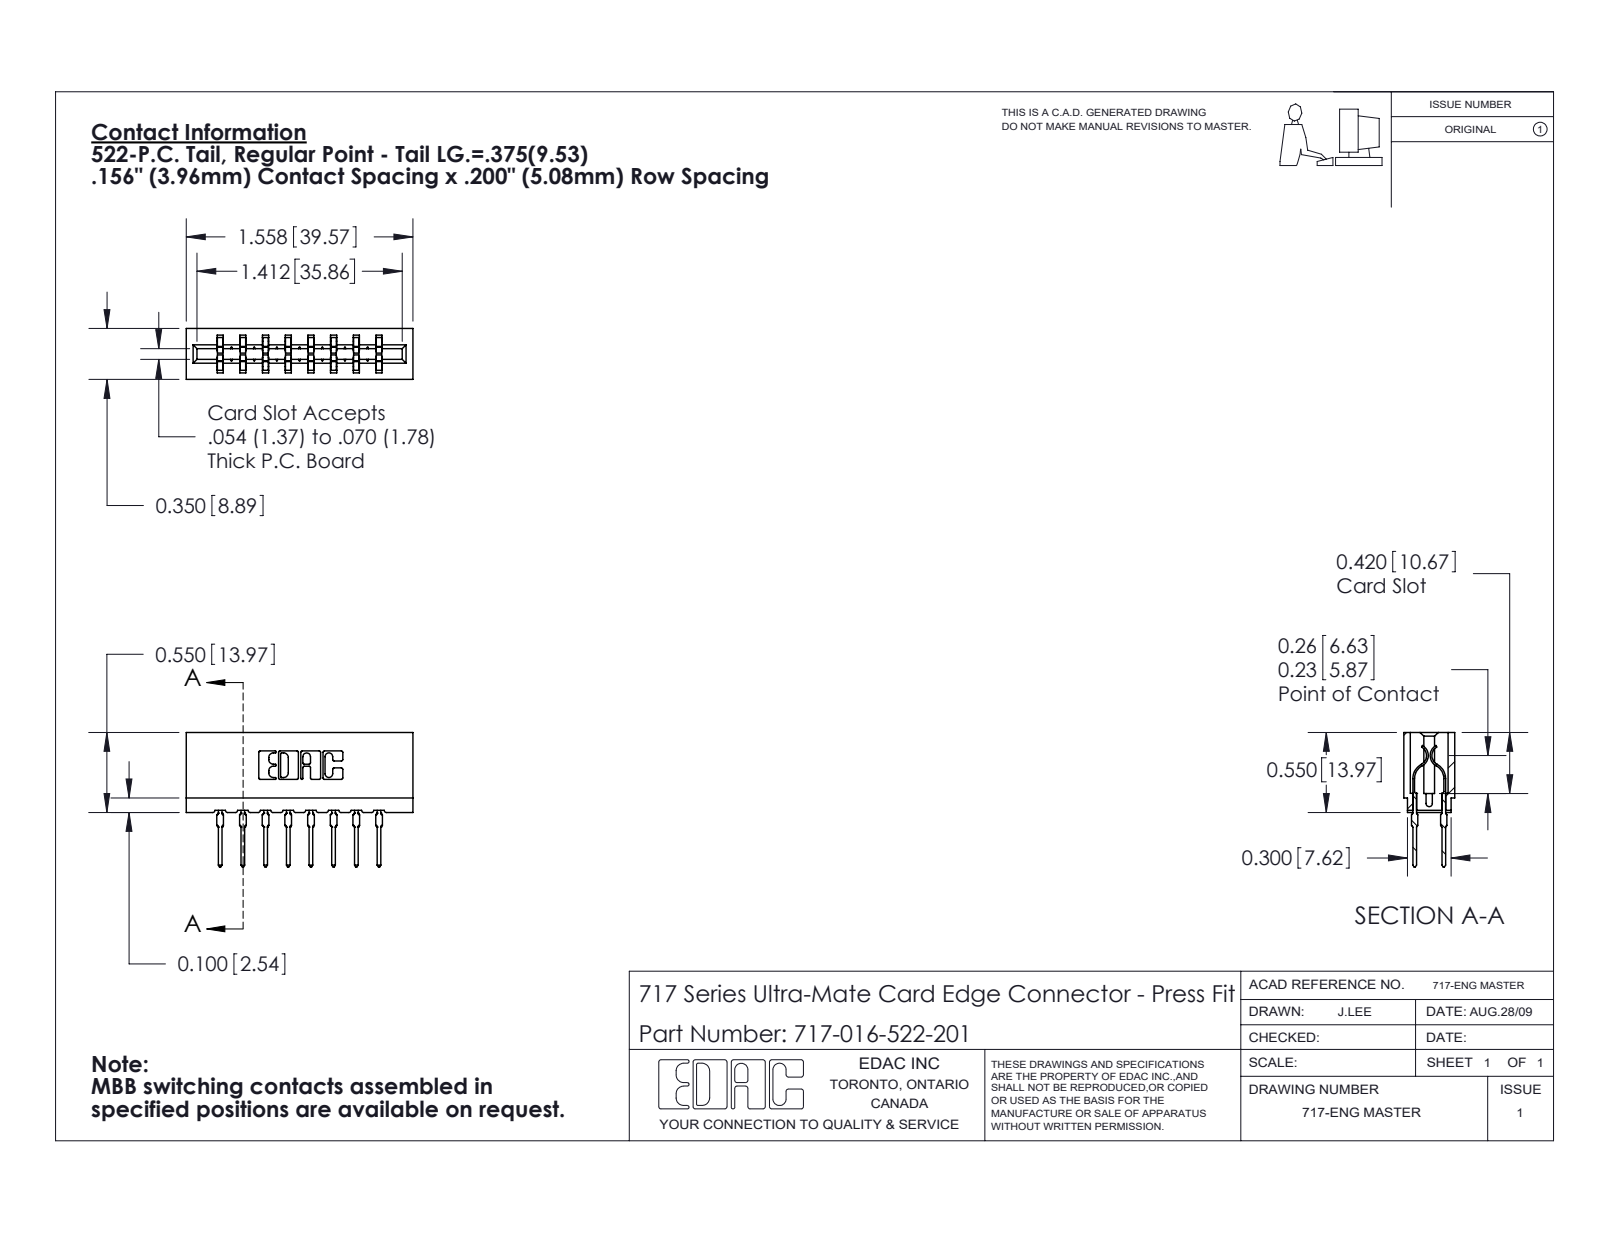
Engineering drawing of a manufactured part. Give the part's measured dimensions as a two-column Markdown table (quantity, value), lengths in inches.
| quantity | value |
| --- | --- |
| part name | 717 Part_Insulator Option - 06; 745-292-001_522; 717-016-522-201 |
| STEP written by | SolidWorks 2020 (CONFIG_CONTROL_DESIGN) |
| units | inches |
| bodies | 17 solids, 1534 faces (798 planar, 320 cylindrical, 416 other) |
| overall size | 1.558 × 0.924 × 0.35 |
| volume | 0.219 in³ |
| surface area | 7.894 in² |
| partial cylindrical surfaces (radius × count) | 0.021 × 32, 0.01 × 22, 0.015 × 16, 0.005 × 8, 0.011 × 8, 0.007 × 6, 0.031 × 6, 0.026 × 3 |
| main face-to-face distances | 0.212, 0.156, 0.138, 0.624, 0.468, 0.198, 0.312, 0.35, 0.042, 0.27 |
